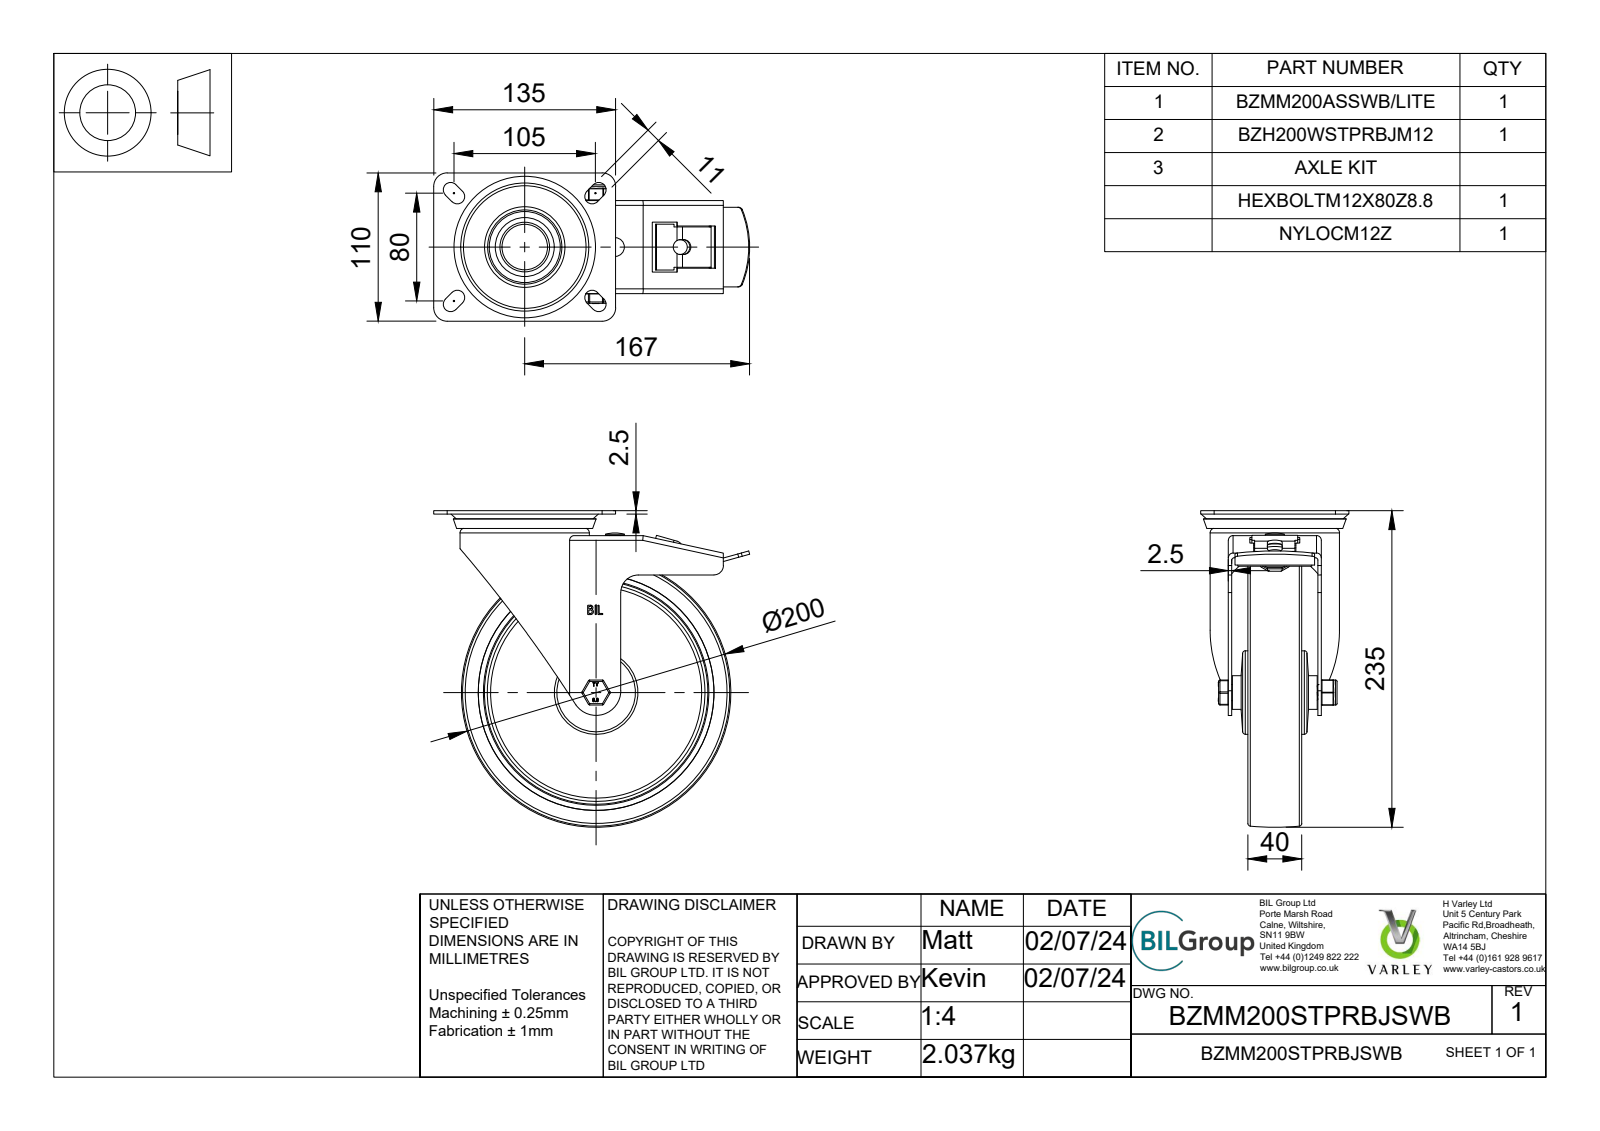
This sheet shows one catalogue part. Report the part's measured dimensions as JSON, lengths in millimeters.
{"part_name": "BZMM200STPRBJSWB v3; BZMM200ASSWB/LITE - 64 v1; ZINC PLATED, PRESSED STEEL TOP PLATE; ZINC PLATED, PRESSED STEEL TOP PLATE Geometry (+7 more)", "step_written_by": "Autodesk Translation Framework v13.14.0.145 (AUTOMOTIVE_DESIGN)", "units": "millimeters", "bodies": {"solids": 68, "faces": 942, "planar": 400, "cylindrical": 212, "other": 330}, "overall_size": [235, 234.5, 110], "volume_mm3": 810987, "surface_area_mm2": 346644, "round_holes": [[8, 1], [11, 1], [12, 1], [12.2, 1], [12.6, 1], [14, 1], [20, 1], [28.5, 1], [30.8, 1], [33.75, 1], [40.3, 1], [40.5, 1]], "round_bosses_or_shafts": [[96, 1], [78, 1], [62, 1], [56.5, 1], [50, 1], [48, 1], [40.8, 1], [39.75, 1]], "partial_cylinders_radius": [[0.5, 18], [1, 12], [5.5, 10], [1.75, 7], [0.25, 6], [2.5, 6], [3.5, 4], [10, 4]], "face_to_face_distances": [6.5, 2.5, 12, 16.75, 23.25, 37.75, 14.5, 31.25, 54.5, 66.5], "hole_center_spacings": [67]}
